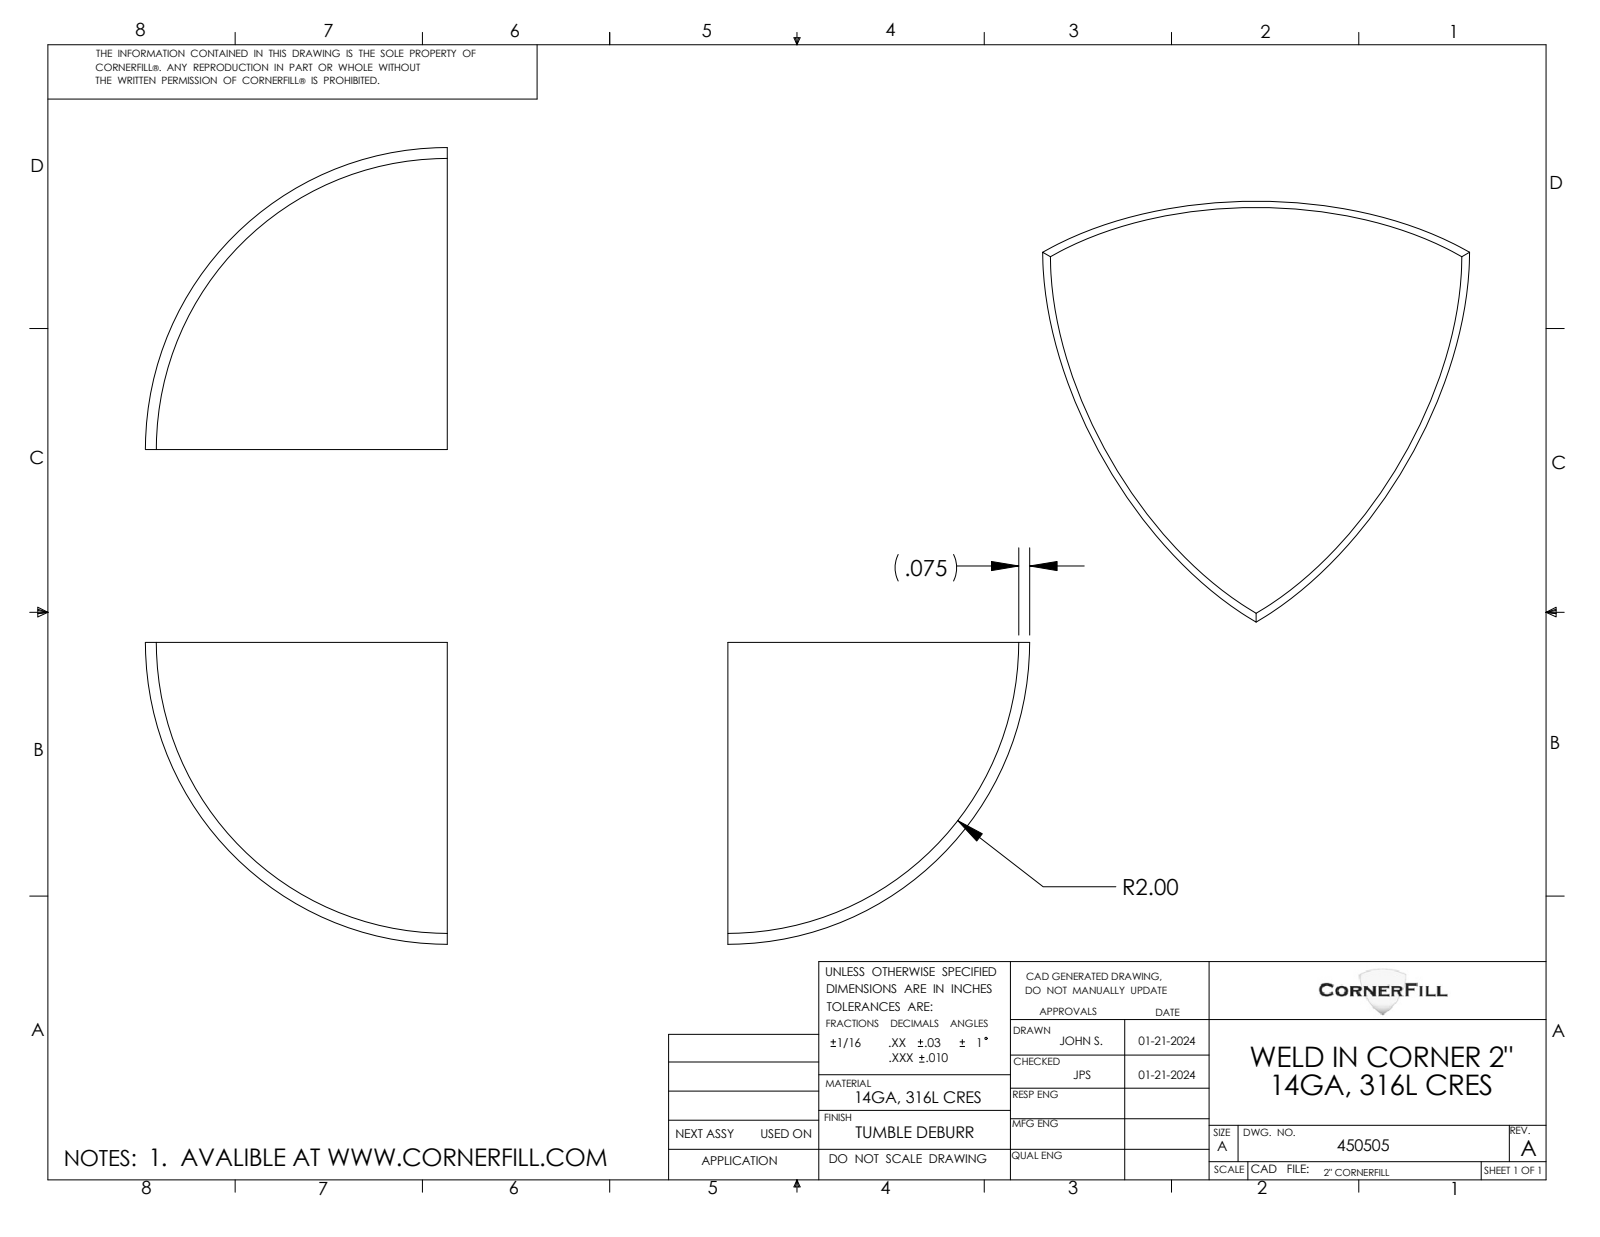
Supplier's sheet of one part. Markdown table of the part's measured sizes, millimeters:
| quantity | value |
| --- | --- |
| part name | 450505 |
| STEP written by | SolidWorks 2021 (CONFIG_CONTROL_DESIGN) |
| units | millimeters |
| bodies | 1 solid, 5 faces (3 planar, 0 cylindrical, 2 other) |
| overall size | 74.5 × 52.7 × 52.7 |
| volume | 8 010 mm³ |
| surface area | 8 884 mm² |
